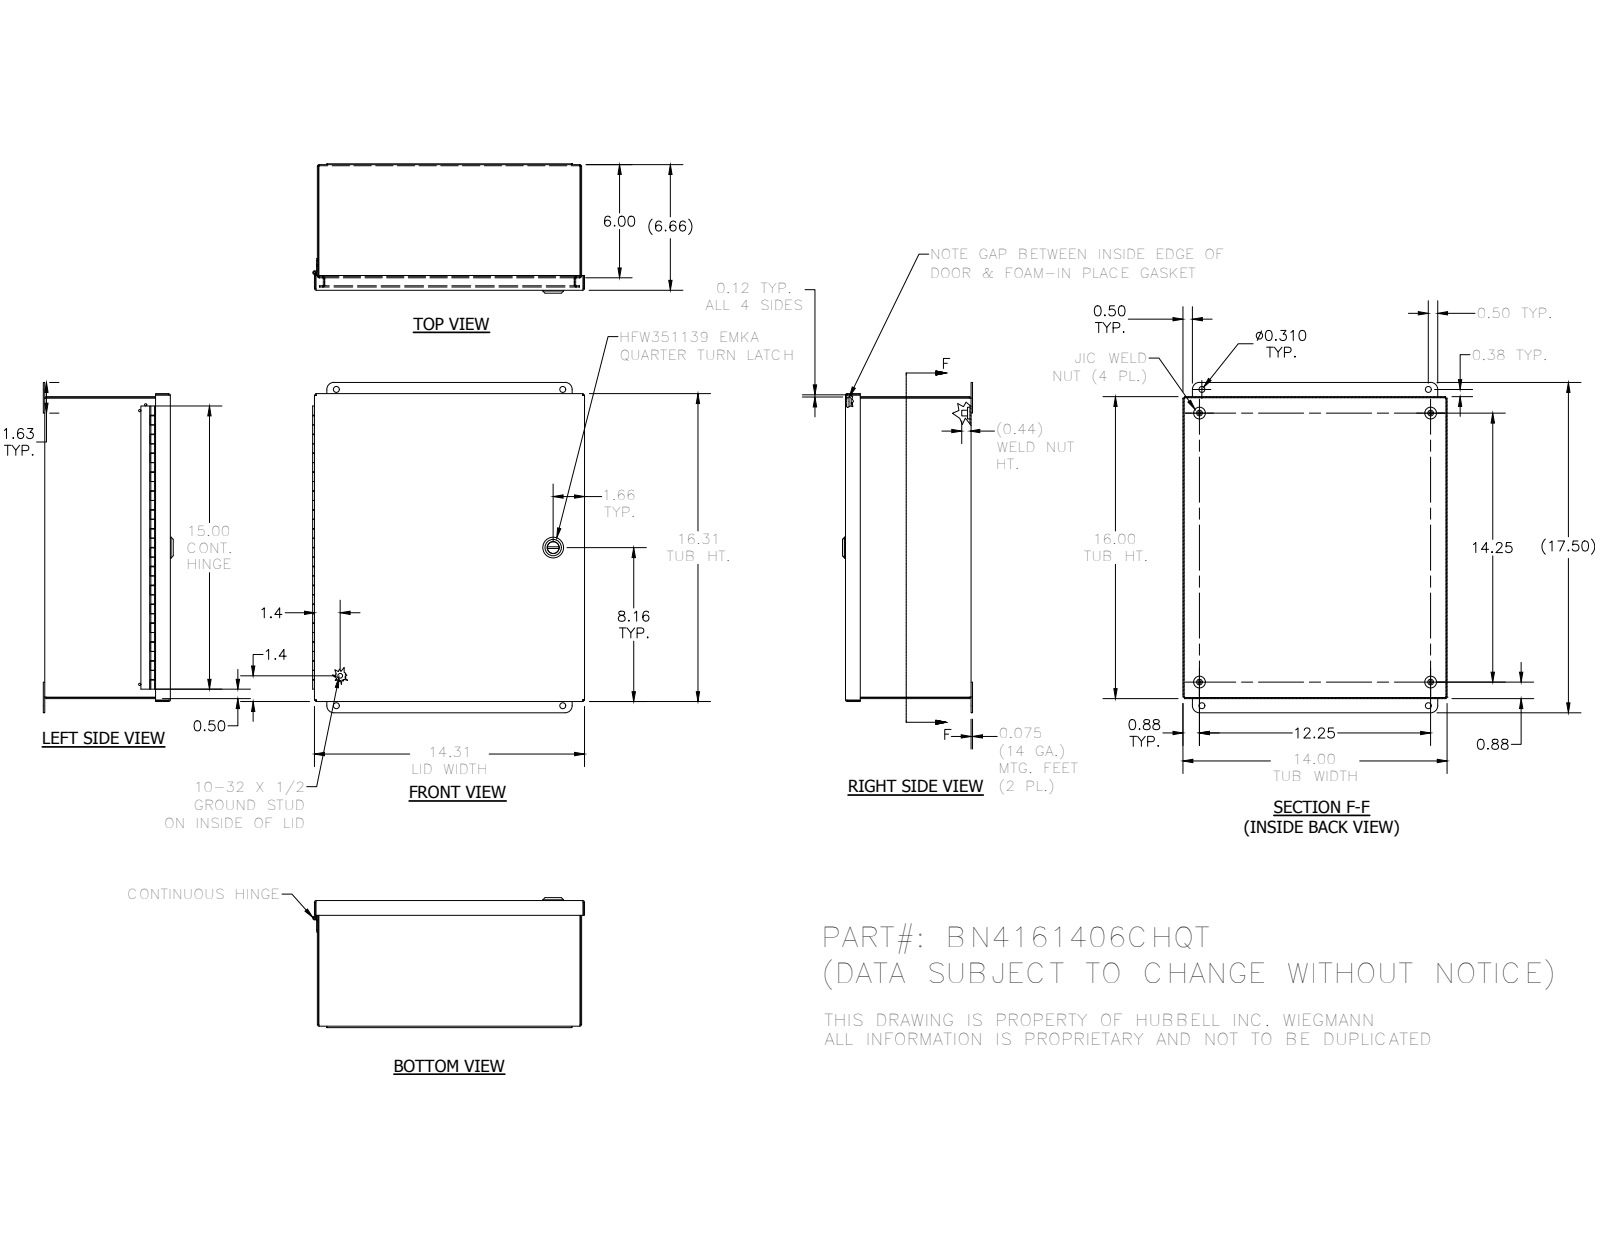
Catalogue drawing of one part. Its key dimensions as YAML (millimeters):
part_name: "BN4161406CHQT"
step_written_by: "SolidWorks 2018 (AUTOMOTIVE_DESIGN)"
units: millimeters
bodies: {solids: 21, faces: 825, planar: 420, cylindrical: 277, other: 128}
overall_size: [444.5, 365.9, 175]
volume: 1096000
surface_area: 1328000
round_holes:
  - {diameter: 4, count: 4}
  - {diameter: 7.9, count: 4}
  - {diameter: 3, count: 3}
  - {diameter: 2.9, count: 1}
  - {diameter: 5, count: 1}
  - {diameter: 8, count: 1}
  - {diameter: 10, count: 1}
  - {diameter: 10.2, count: 1}
  - {diameter: 16.1, count: 1}
  - {diameter: 20.4, count: 1}
round_bosses_or_shafts:
  - {diameter: 7.6, count: 4}
  - {diameter: 15.9, count: 2}
  - {diameter: 15.9, count: 2}
  - {diameter: 28, count: 1}
  - {diameter: 22, count: 1}
  - {diameter: 19.8, count: 1}
  - {diameter: 15.8, count: 1}
  - {diameter: 15.2, count: 1}
partial_cylinders:
  - {radius: 0.3, count: 30}
  - {radius: 0.8, count: 20}
  - {radius: 2.4, count: 20}
  - {radius: 3.2, count: 16}
  - {radius: 0.5, count: 12}
  - {radius: 4, count: 4}
  - {radius: 9.5, count: 4}
  - {radius: 0.4, count: 2}
face_to_face_distances: [1.6, 1.6, 167.5, 169.1, 165.9, 167.5, 404.8, 355.6, 354, 354]
hole_center_spacings: [499.8, 31.9, 304.8, 309.6, 309.6, 311.2, 362, 393.7]
